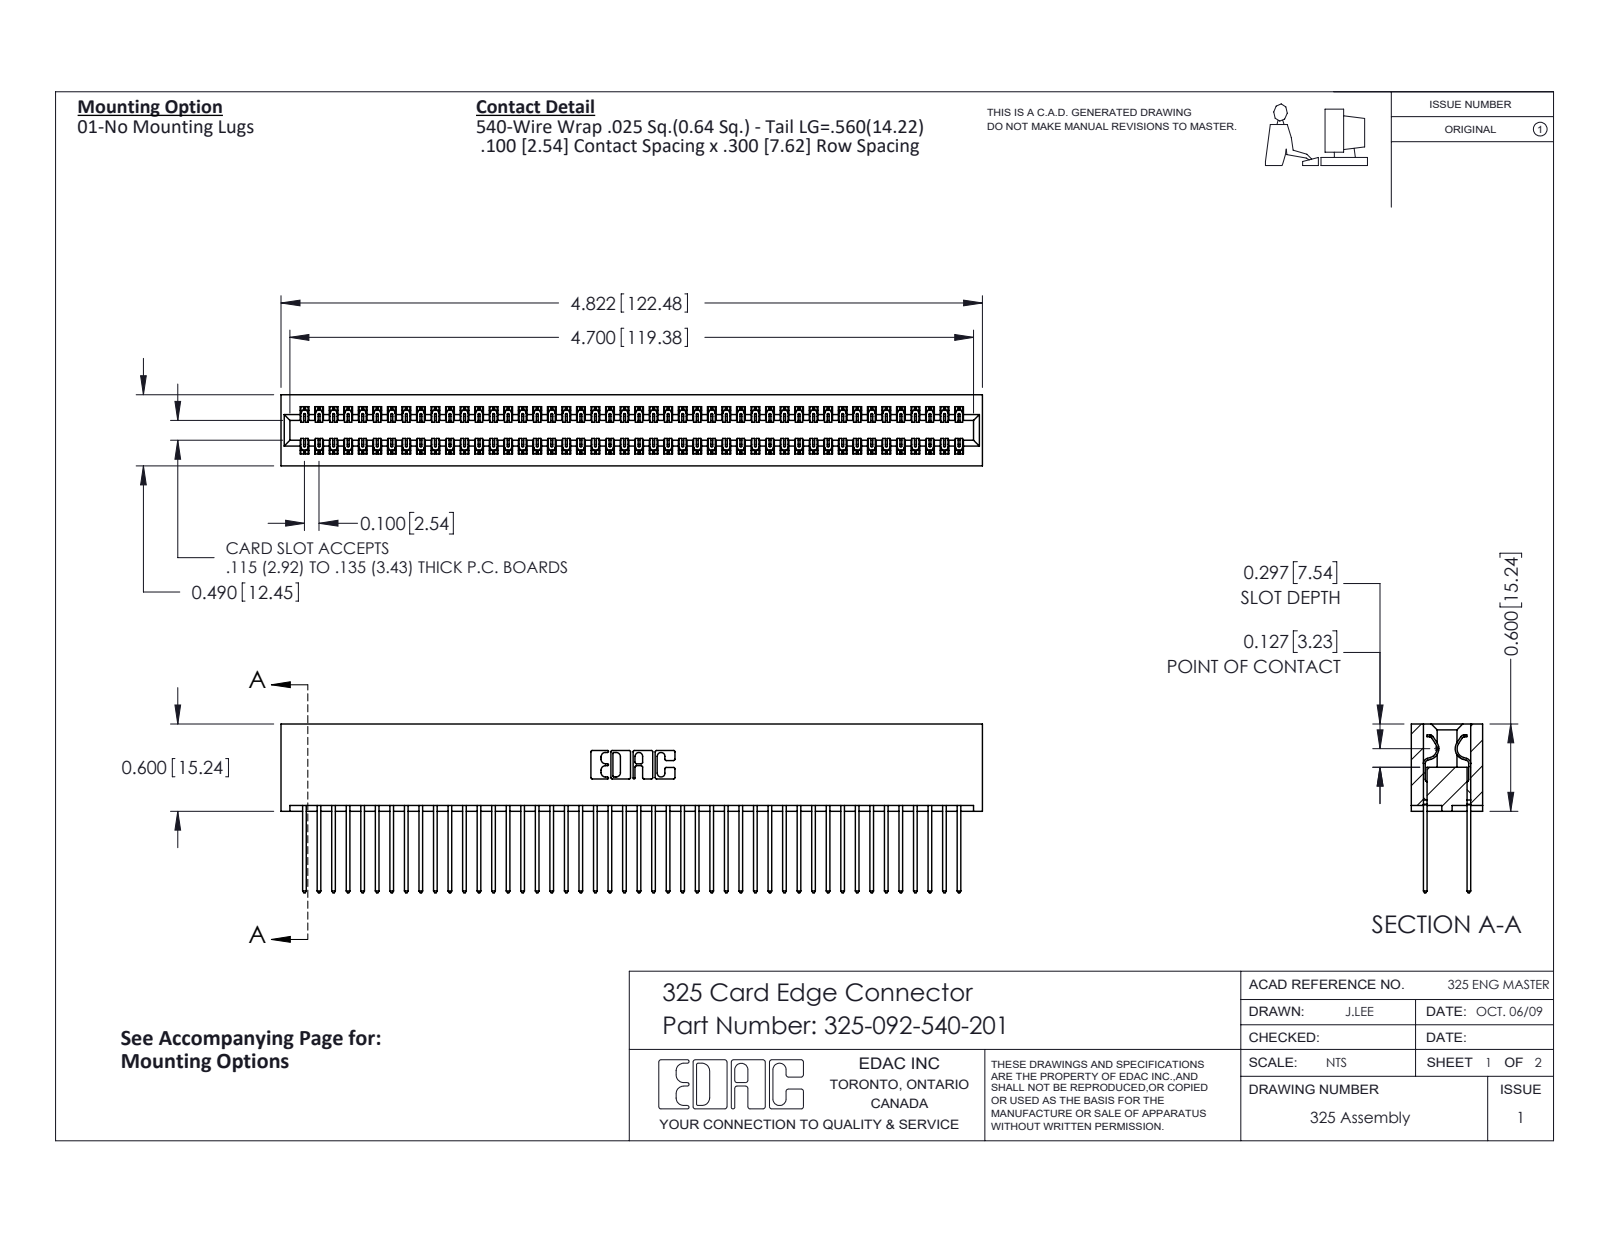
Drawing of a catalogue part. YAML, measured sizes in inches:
part_name: "325 Part_Lugless; 325-292-001_325-293-140; 325-092-540-201"
step_written_by: "SolidWorks 2016 (CONFIG_CONTROL_DESIGN)"
units: inches
bodies: {solids: 93, faces: 4890, planar: 3378, cylindrical: 1512, other: 0}
overall_size: [4.822, 1.16, 0.49]
volume: 1.025
surface_area: 35.27
partial_cylinders:
  - {radius: 0.006, count: 138}
  - {radius: 0.01, count: 92}
  - {radius: 0.01, count: 22}
  - {radius: 0.007, count: 6}
  - {radius: 0.031, count: 6}
  - {radius: 0.026, count: 3}
  - {radius: 0.014, count: 2}
  - {radius: 0.022, count: 2}
face_to_face_distances: [0.083, 0.407, 0.3, 0.107, 0.383, 0.025, 0.325, 0.49, 0.275, 0.56]
